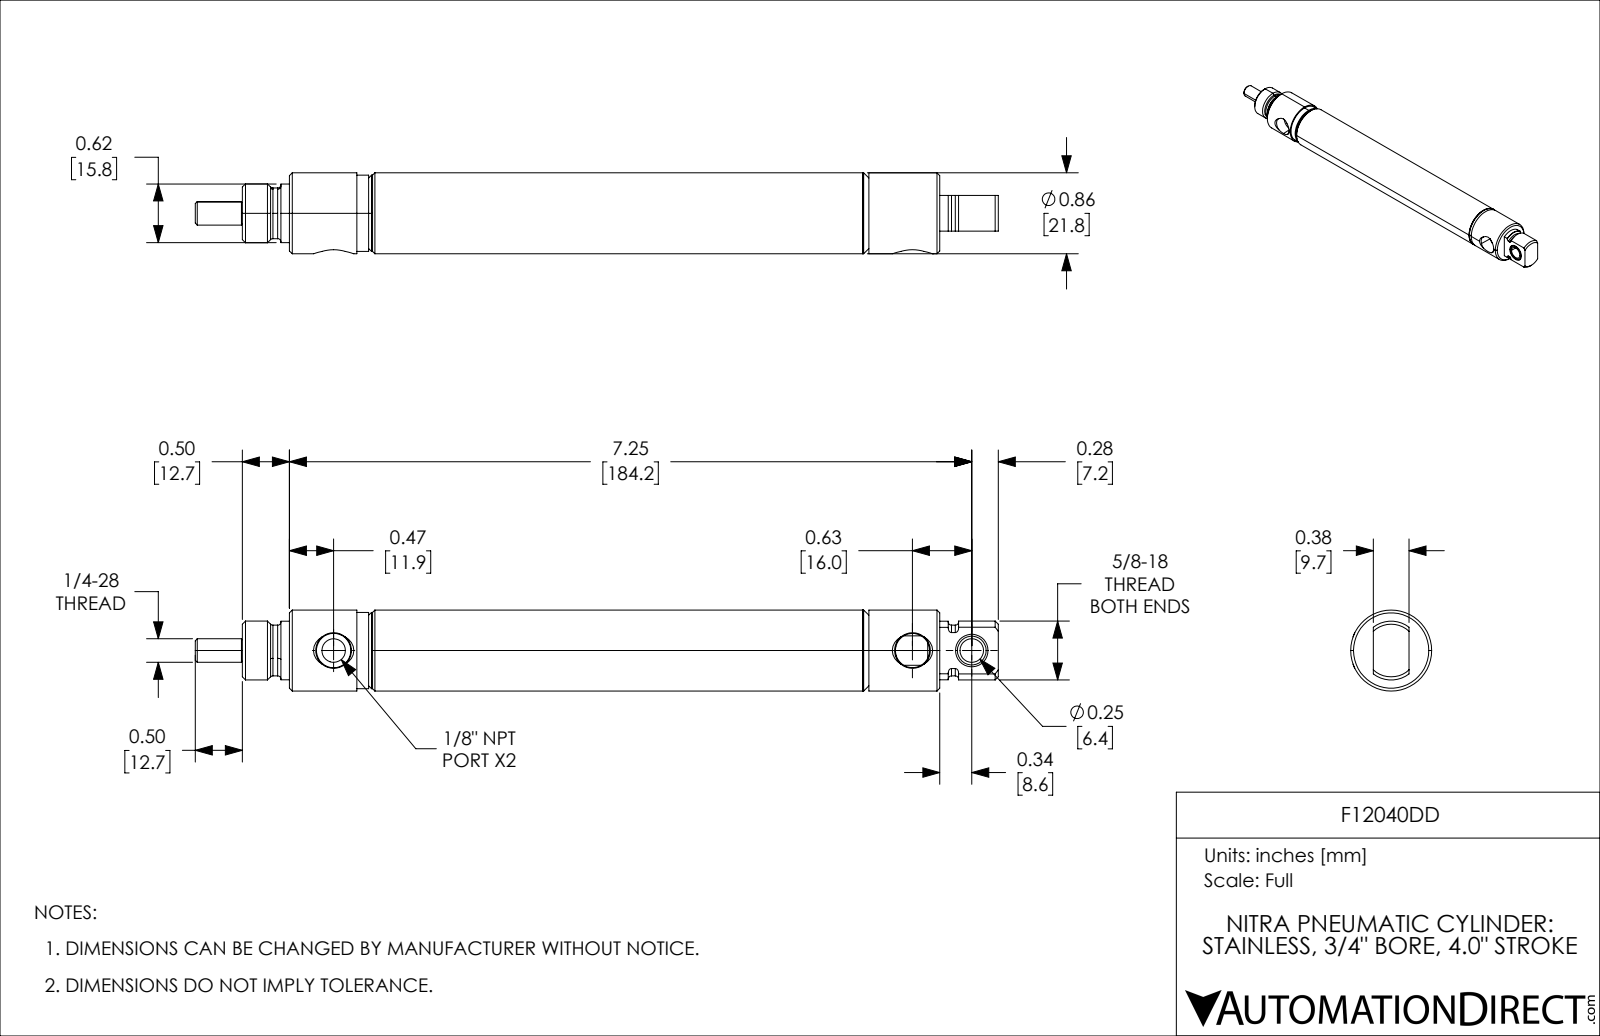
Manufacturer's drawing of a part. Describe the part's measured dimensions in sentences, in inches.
The part is named "F12040DD_7; F12040DD_3; F12040DD; F12040DD_11 (+2 more)". Its 3-D file was written by "SolidWorks 2021 (CONFIG_CONTROL_DESIGN)". It is 5 solids with 158 faces: 29 planar, 61 cylindrical and 68 other. Overall it measures 8.532 by 0.86 by 0.86 inches. Its volume is 2.483 cubic inches and its surface area 49 square inches. Round holes: 1 of diameter 0.25, 1 of diameter 0.251, 1 of diameter 0.274, 1 of diameter 0.312, 1 of diameter 0.346, 1 of diameter 0.363, 1 of diameter 0.5, 1 of diameter 0.702. Round bosses or shafts: 1 of diameter 0.86, 1 of diameter 0.81, 1 of diameter 0.762, 1 of diameter 0.625, 1 of diameter 0.622, 1 of diameter 0.539, 1 of diameter 0.25, 1 of diameter 0.23. Partial cylindrical surfaces (rounded edges, fillets, slot ends): 1 of radius 0.269. The main face-to-face distances are 0.844, 1.594, 6.438, 4, 4.844, 5.816, 1.816, 0.972, 0.5, 0.38. The hole center spacings are 0.63, 6.15, 6.78.
